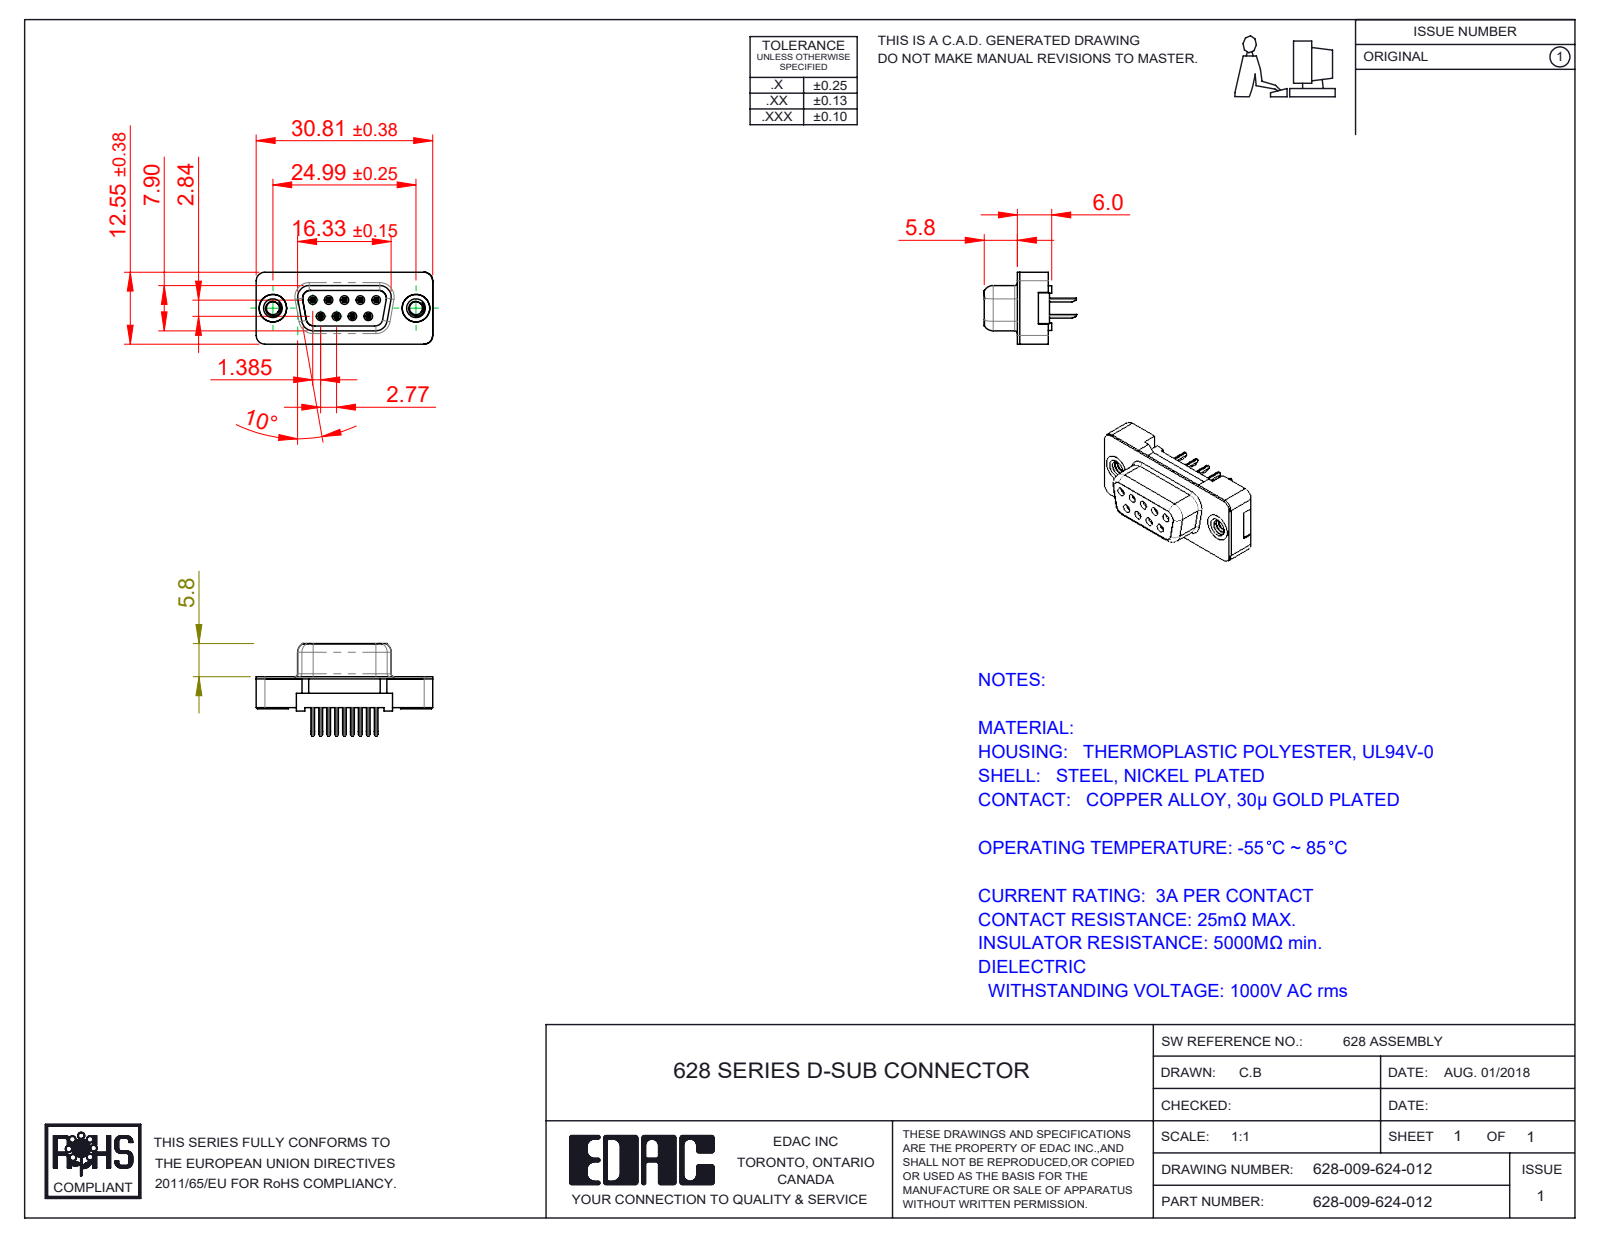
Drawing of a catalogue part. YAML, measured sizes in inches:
part_name: "628 PB Shell_09 Contacts; 628 PB Contact Row 2_24; 628 Plastic Body Housing_09 Contacts; 628 PB 4-40 Threaded Rivet (+2 more)"
step_written_by: "SolidWorks 2020 (CONFIG_CONTROL_DESIGN)"
units: inches
bodies: {solids: 13, faces: 911, planar: 378, cylindrical: 248, other: 285}
overall_size: [1.213, 0.634, 0.494]
volume: 0.12
surface_area: 6.868
round_holes:
  - {diameter: 0.035, count: 9}
  - {diameter: 0.089, count: 2}
  - {diameter: 0.12, count: 2}
  - {diameter: 0.157, count: 2}
  - {diameter: 0.189, count: 2}
  - {diameter: 0.197, count: 2}
round_bosses_or_shafts:
  - {diameter: 0.193, count: 2}
partial_cylinders:
  - {radius: 0.01, count: 36}
  - {radius: 0.02, count: 13}
  - {radius: 0.053, count: 11}
  - {radius: 0.012, count: 9}
  - {radius: 0.059, count: 8}
  - {radius: 0.035, count: 4}
  - {radius: 0.063, count: 4}
  - {radius: 0.069, count: 4}
face_to_face_distances: [0.016, 0.079, 0.218, 0.109, 0.098, 0.197, 0.213, 0.244, 0.343, 0.297]
hole_center_spacings: [0.124, 0.109, 0.218, 0.198, 0.198, 0.327, 0.28, 0.294]
